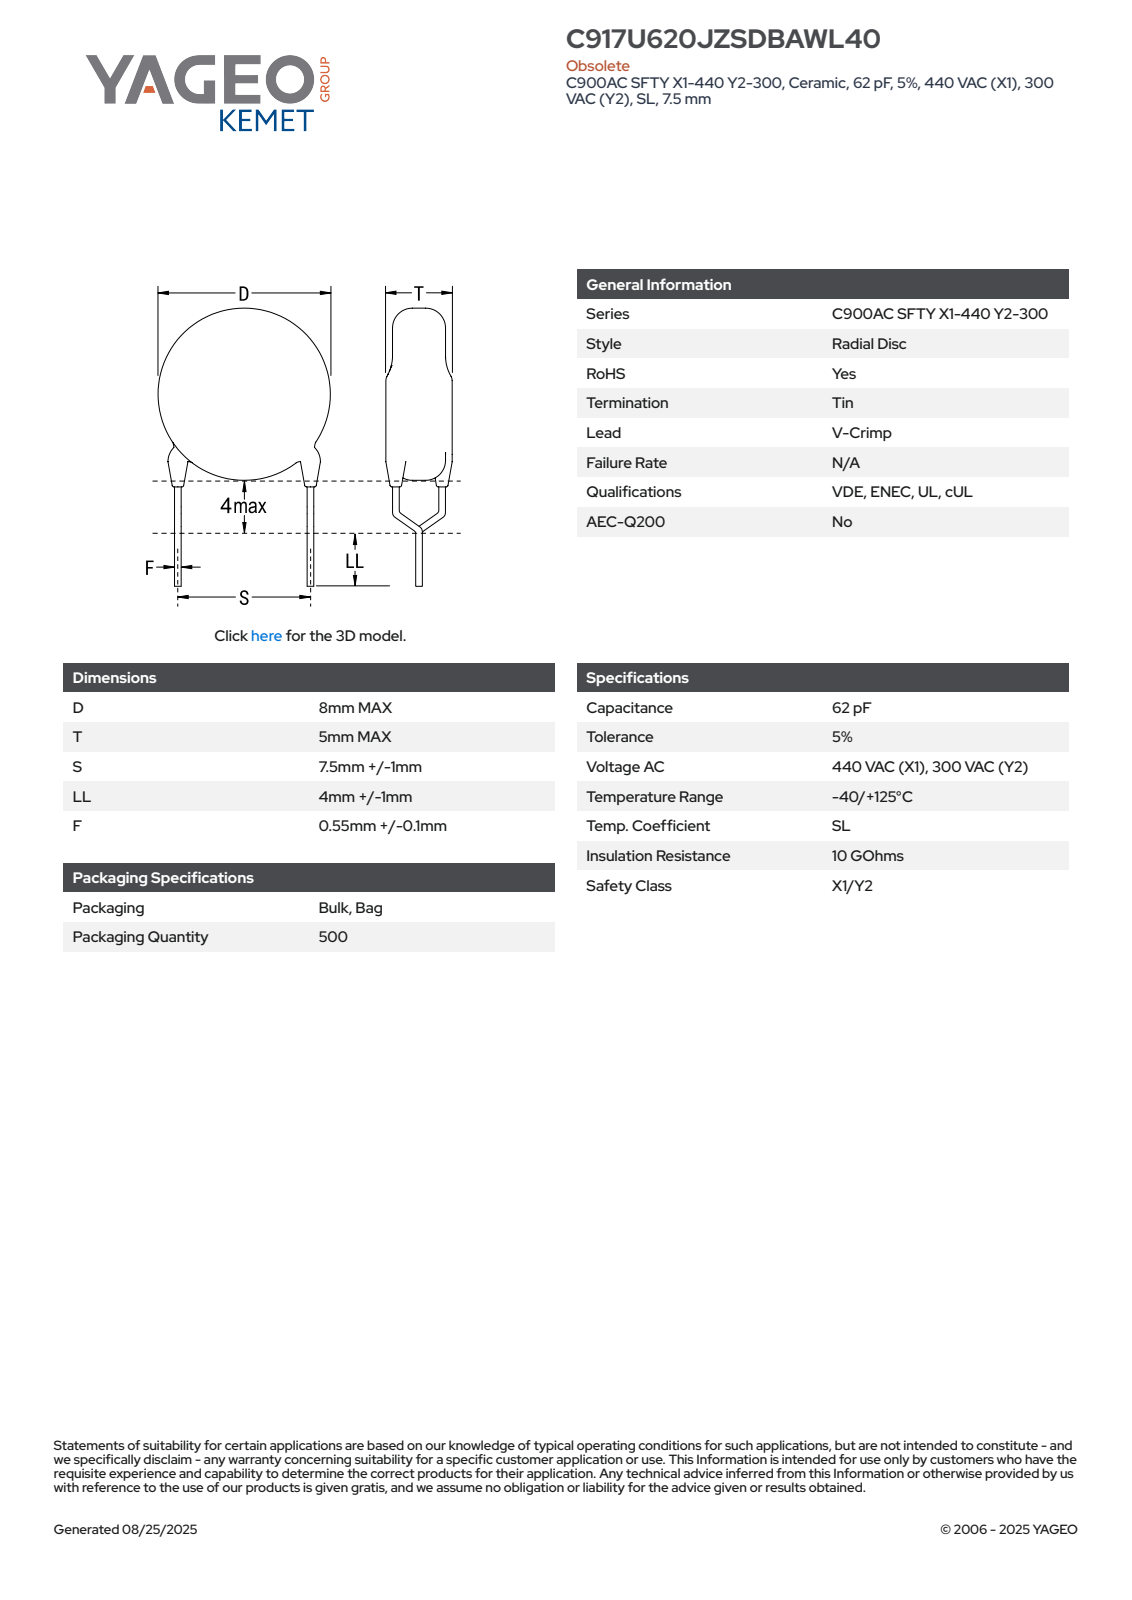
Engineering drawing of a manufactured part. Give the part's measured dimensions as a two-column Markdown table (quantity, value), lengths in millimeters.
| quantity | value |
| --- | --- |
| part name | CCD_VCC900_D8T5S7.5LL5F0.65 |
| STEP written by | SolidWorks 2014 (AUTOMOTIVE_DESIGN) |
| units | millimeters |
| bodies | 5 solids, 93 faces (65 planar, 16 cylindrical, 12 other) |
| overall size | 16.8 × 8.15 × 5 |
| volume | 250 mm³ |
| surface area | 258 mm² |
| round bosses / shafts (diameter × count) | 0.65 × 6, 8 × 1 |
| main face-to-face distances | 5, 7.9, 1.04, 13.32, 5.42, 12.28, 4.38, 0.84, 0.45, 0.39 |
